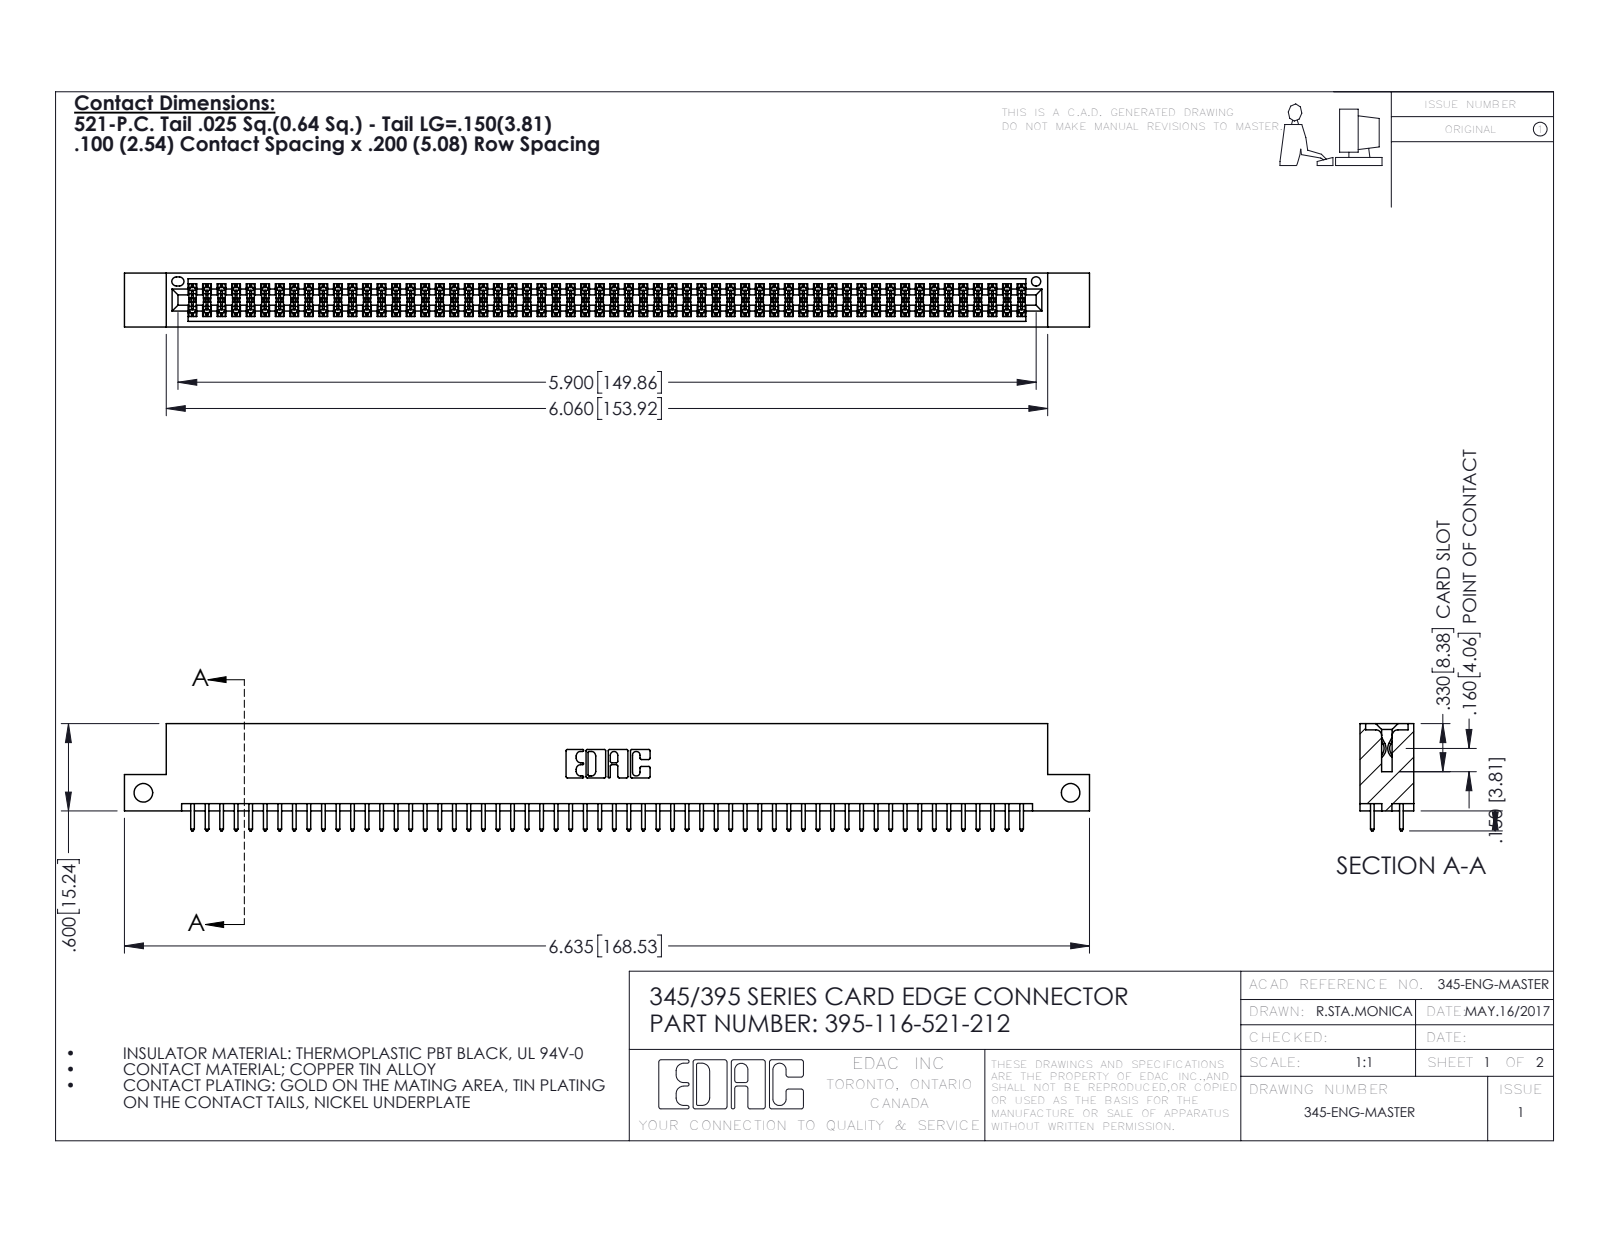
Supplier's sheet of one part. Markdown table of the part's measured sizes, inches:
| quantity | value |
| --- | --- |
| part name | 395-116-521-212; 345 Part_Flush Mounting Lugs - Side Mount; 345-292-001_345-293-121 |
| STEP written by | SolidWorks 2016 (CONFIG_CONTROL_DESIGN) |
| units | inches |
| bodies | 117 solids, 5926 faces (3908 planar, 2018 cylindrical, 0 other) |
| overall size | 6.635 × 0.737 × 0.37 |
| volume | 1 in³ |
| surface area | 37.33 in² |
| round holes (diameter × count) | 0.128 × 2, 0.064 × 1 |
| partial cylindrical surfaces (radius × count) | 0.006 × 174, 0.01 × 116, 0.01 × 22, 0.007 × 6, 0.031 × 6, 0.026 × 3, 0.014 × 2, 0.019 × 2 |
| main face-to-face distances | 0.298, 0.072, 0.2, 0.098, 0.272, 0.025, 0.37, 0.225, 0.175, 0.149 |
| hole center spacings | 6.375 |
